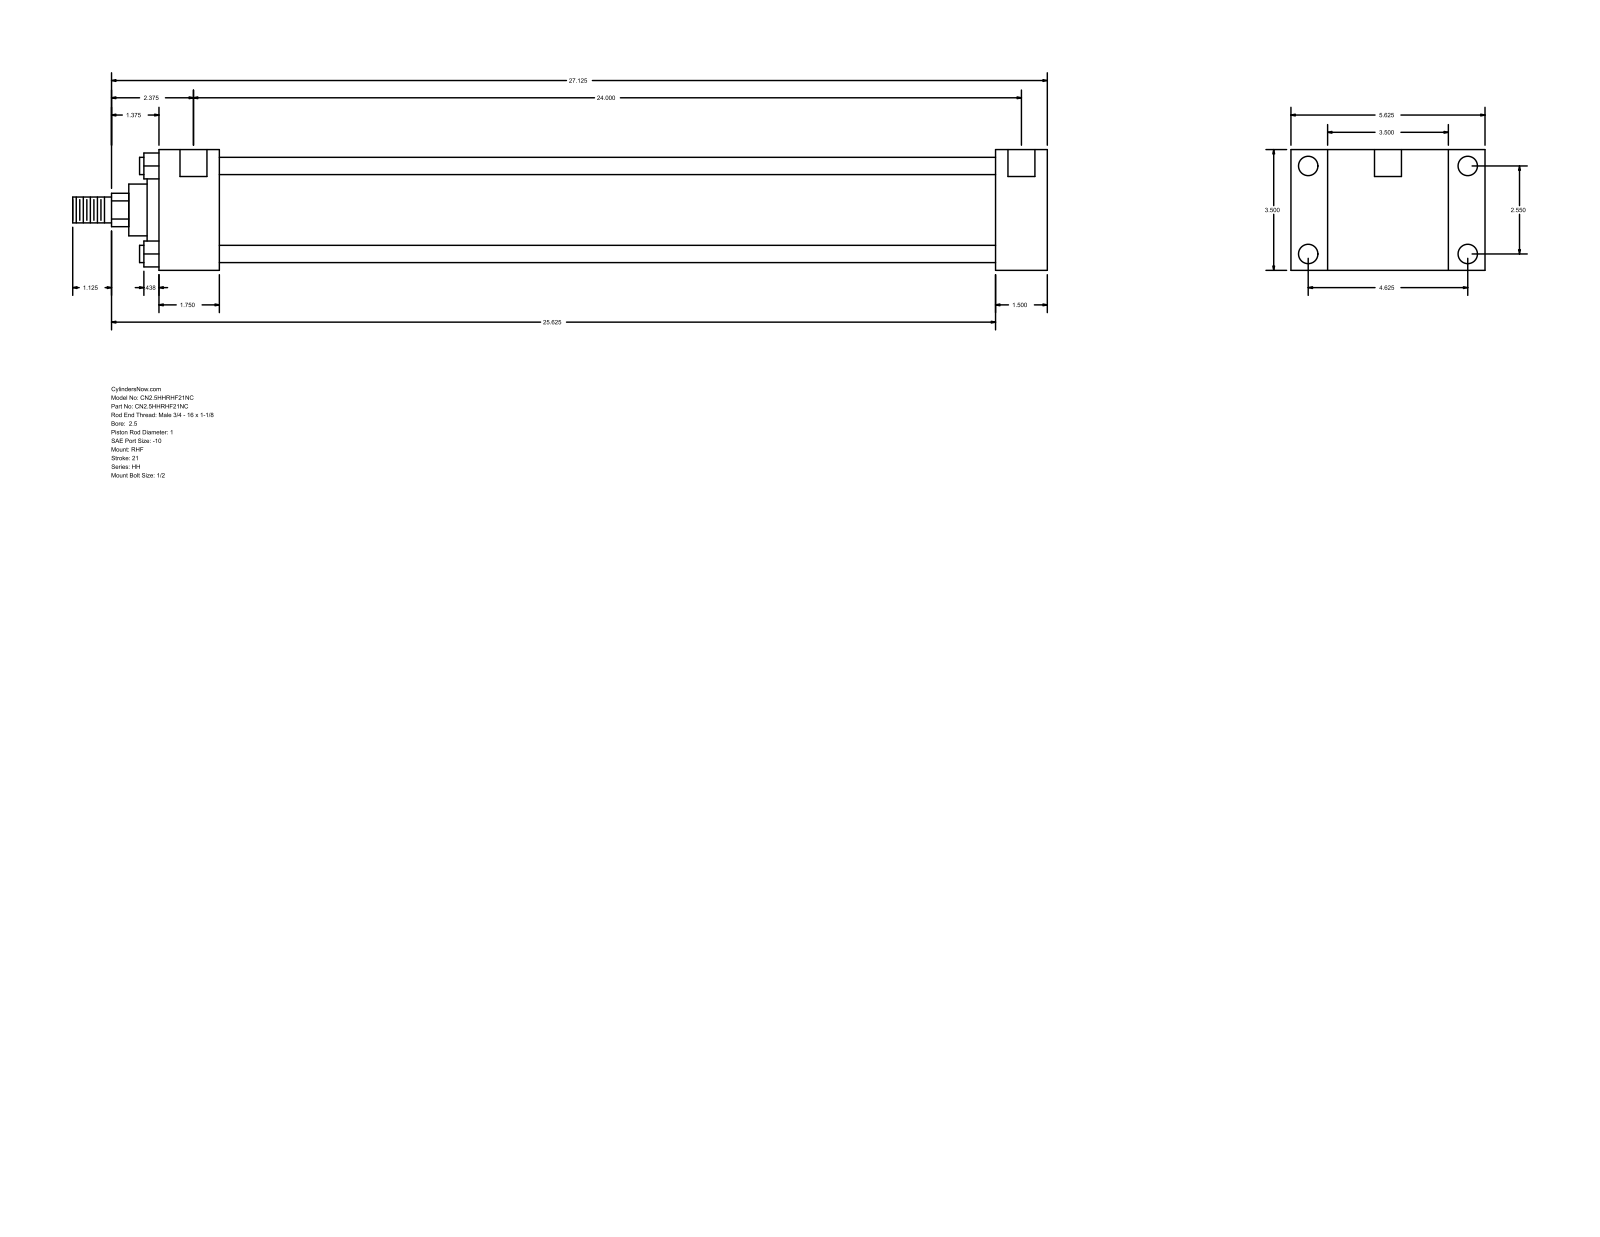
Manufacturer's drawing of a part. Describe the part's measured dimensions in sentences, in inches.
The part is named "HH_RHF__0250_1". Its 3-D file was written by "GSSL Pune (CONFIG_CONTROL_DESIGN)". It is 0 solids with 90 faces: 61 planar, 29 cylindrical and 0 other. Overall it measures 28.25 by 5.625 by 3.5 inches. Round holes: 4 of diameter 0.219, 4 of diameter 0.563, 2 of diameter 0.781. Round bosses or shafts: 4 of diameter 0.5, 1 of diameter 2.875, 1 of diameter 2.375, 1 of diameter 1.5, 1 of diameter 1, 1 of diameter 0.75. Partial cylindrical surfaces (rounded edges, fillets, slot ends): 1 of radius 0.484. The main face-to-face distances are 3.5, 1.5, 1.063, 4.563, 24.25, 25.75, 5.625, 1.75, 22.5, 24. The hole center spacings are 0.063, 2.55, 4.625, 5.281, 24.062, 24.125, 24.
